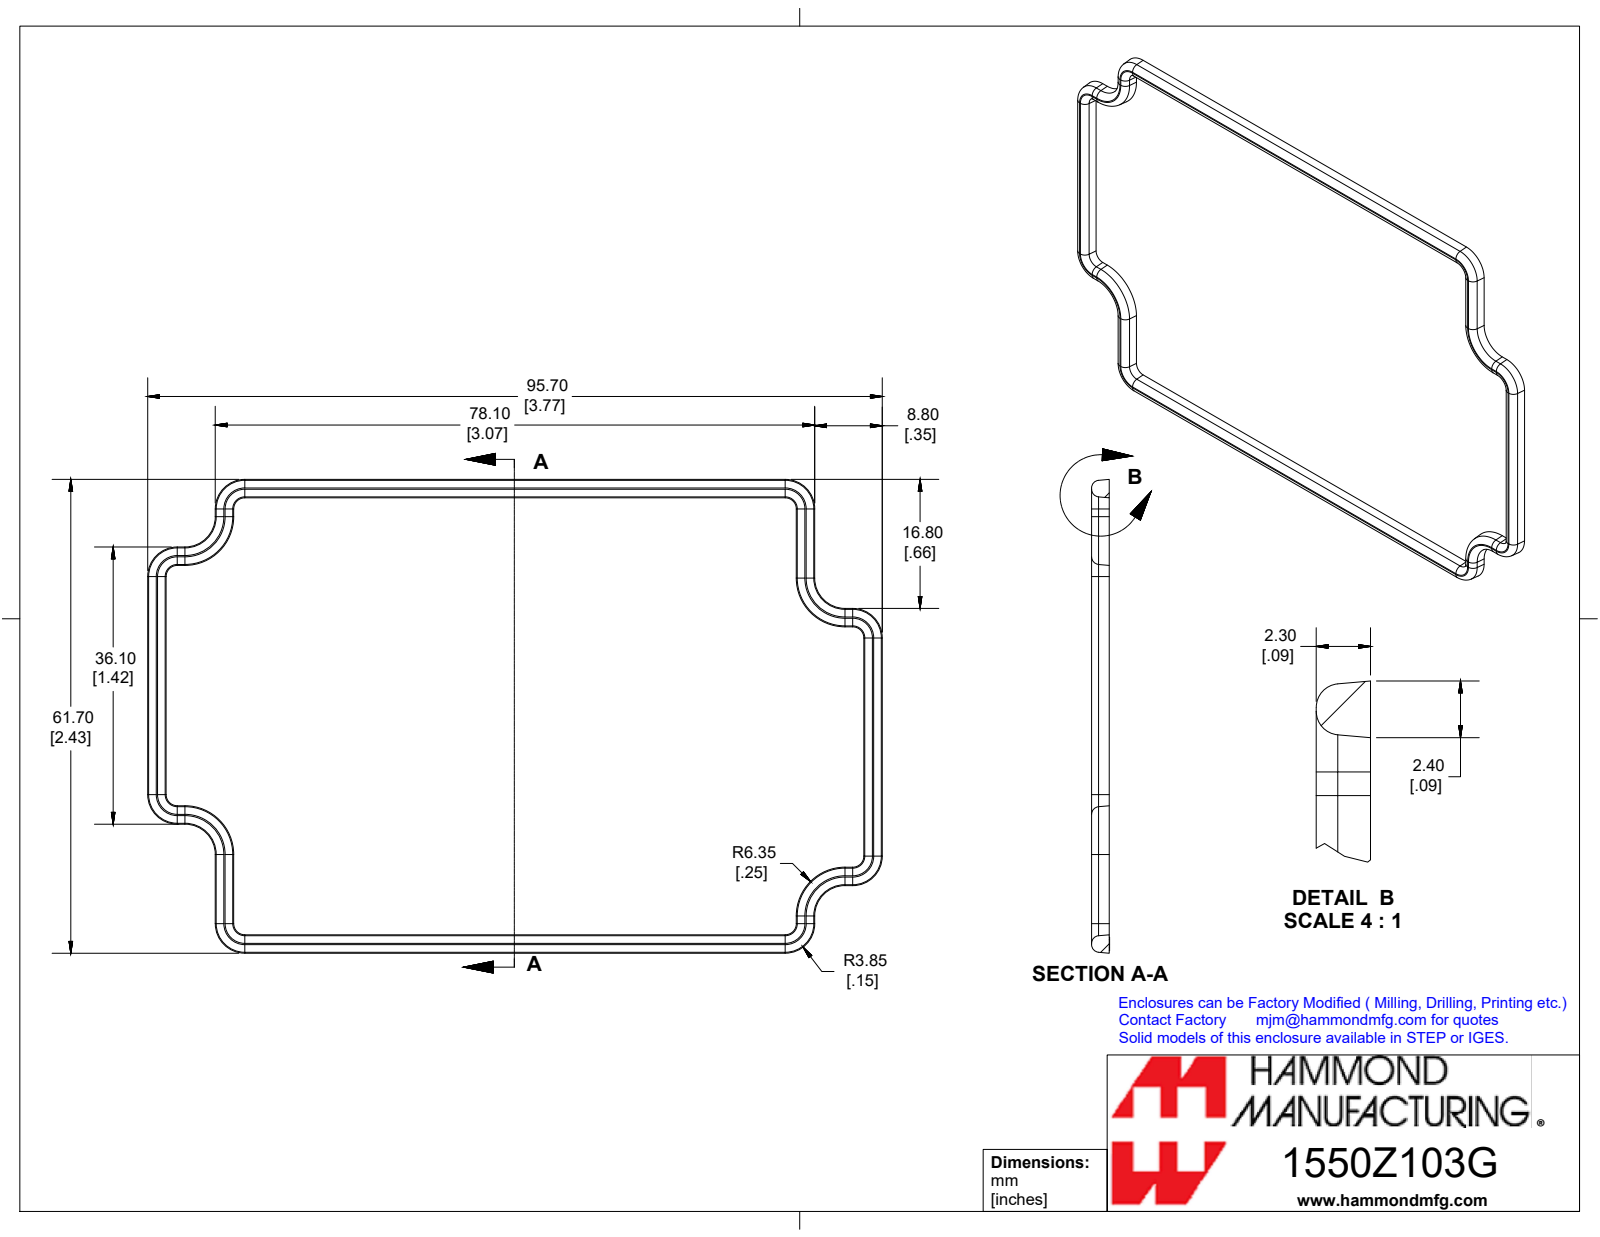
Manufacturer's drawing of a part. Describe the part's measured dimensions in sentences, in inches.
The part is named "1550Z103GASKET". Its 3-D file was written by "SolidWorks 2019 (CONFIG_CONTROL_DESIGN)". It is 1 solid with 158 faces: 40 planar, 24 cylindrical and 94 other. Overall it measures 3.768 by 2.429 by 0.093 inches. Its volume is 0.083 cubic inches and its surface area 3.705 square inches. Partial cylindrical surfaces (rounded edges, fillets, slot ends): 20 of radius 0.039. The main face-to-face distances are 2.326, 3.659, 0.345, 3.313, 0.091, 2.968, 1.98, 0.659, 1.667, 0.314.
